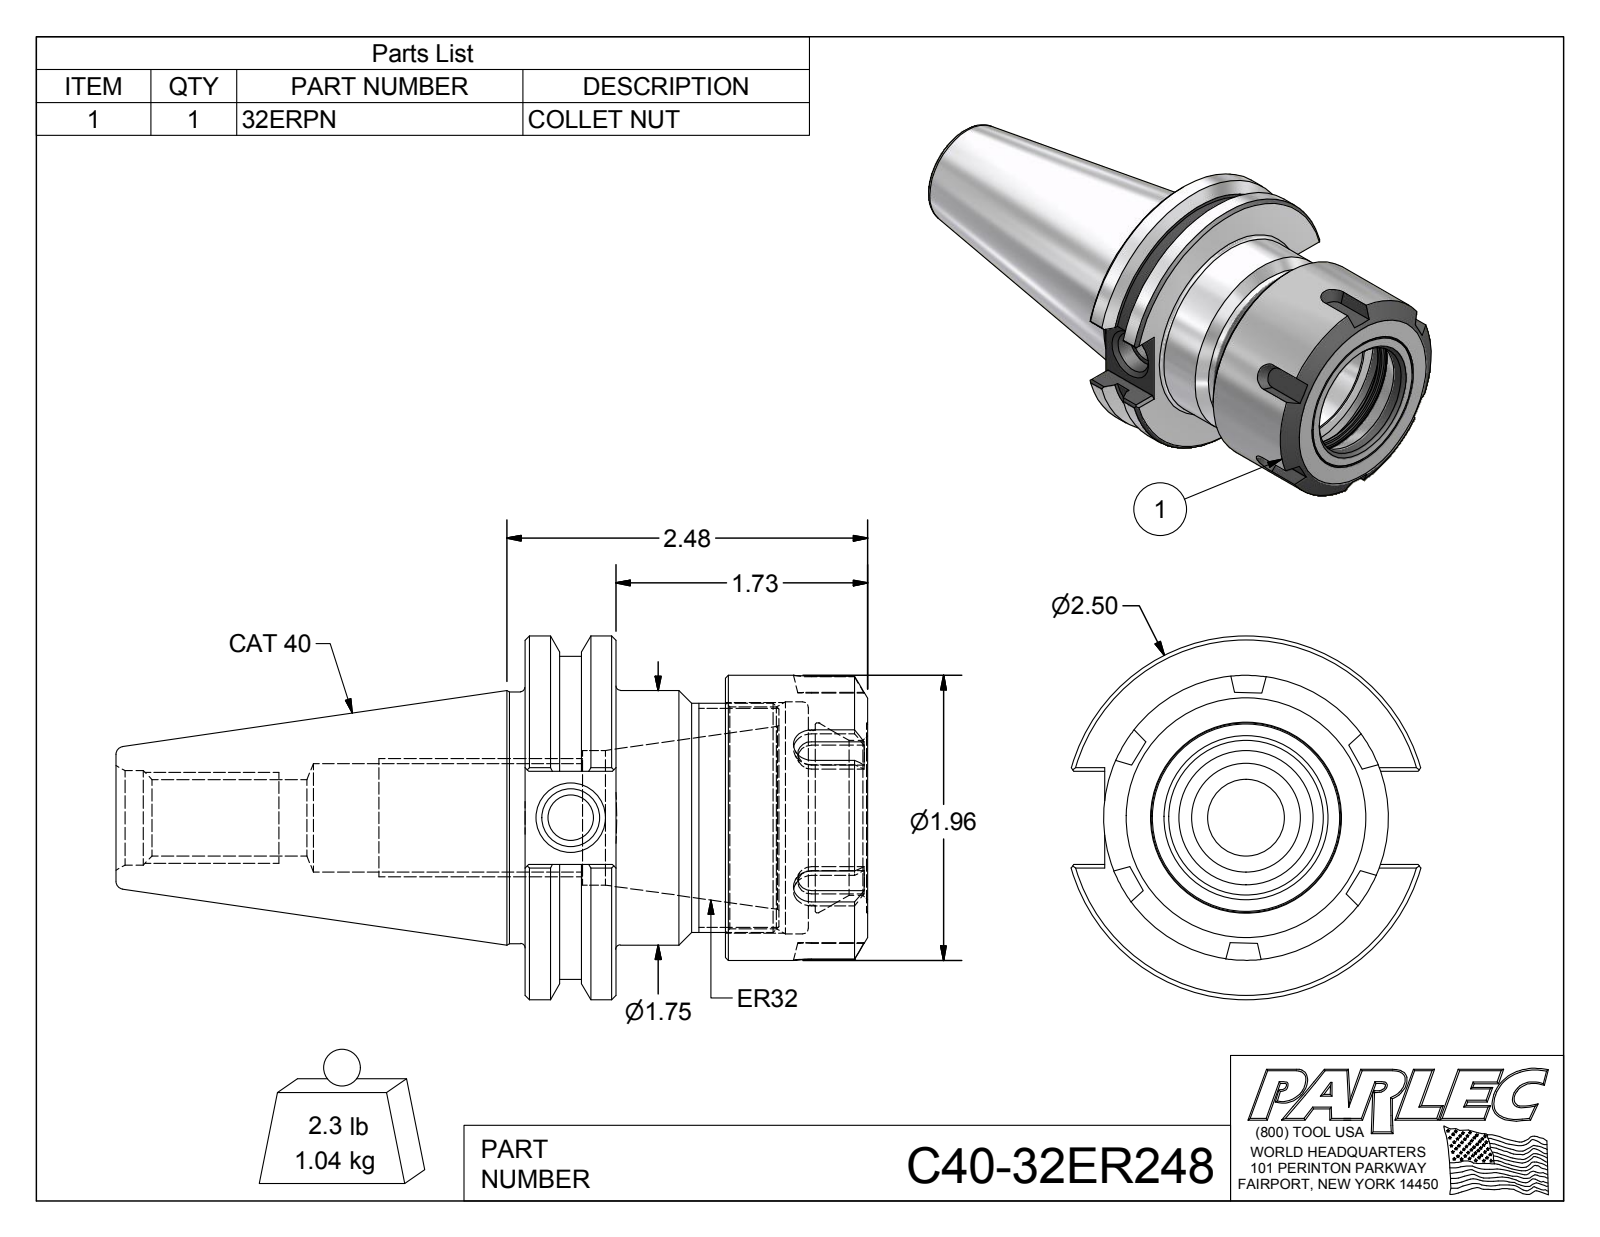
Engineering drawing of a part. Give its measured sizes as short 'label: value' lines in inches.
name: C40-32ER248; C40-32ER236-1; 32ERPN
written by: Autodesk Inventor 2012 (AUTOMOTIVE_DESIGN)
unit: in
bodies: 2 solids, 117 faces (55 planar, 21 cylindrical, 41 other)
size: 5.168 × 2.5 × 2.403
volume: 8.265 in³; area: 56 in²
holes: 1× ⌀0.315, 1× ⌀0.396, 1× ⌀0.527, 1× ⌀0.648, 1× ⌀0.745, 1× ⌀0.925, 1× ⌀1.063, 1× ⌀1.2, 1× ⌀1.305, 1× ⌀1.523, 1× ⌀1.595
bosses: 1× ⌀2.5, 1× ⌀2.219, 1× ⌀1.958, 1× ⌀1.75, 1× ⌀1.73, 1× ⌀1.575
face distances: 0.625, 2.355, 1.73, 1.377, 0.752, 0.978, 1.948, 1.323, 0.571, 0.407
